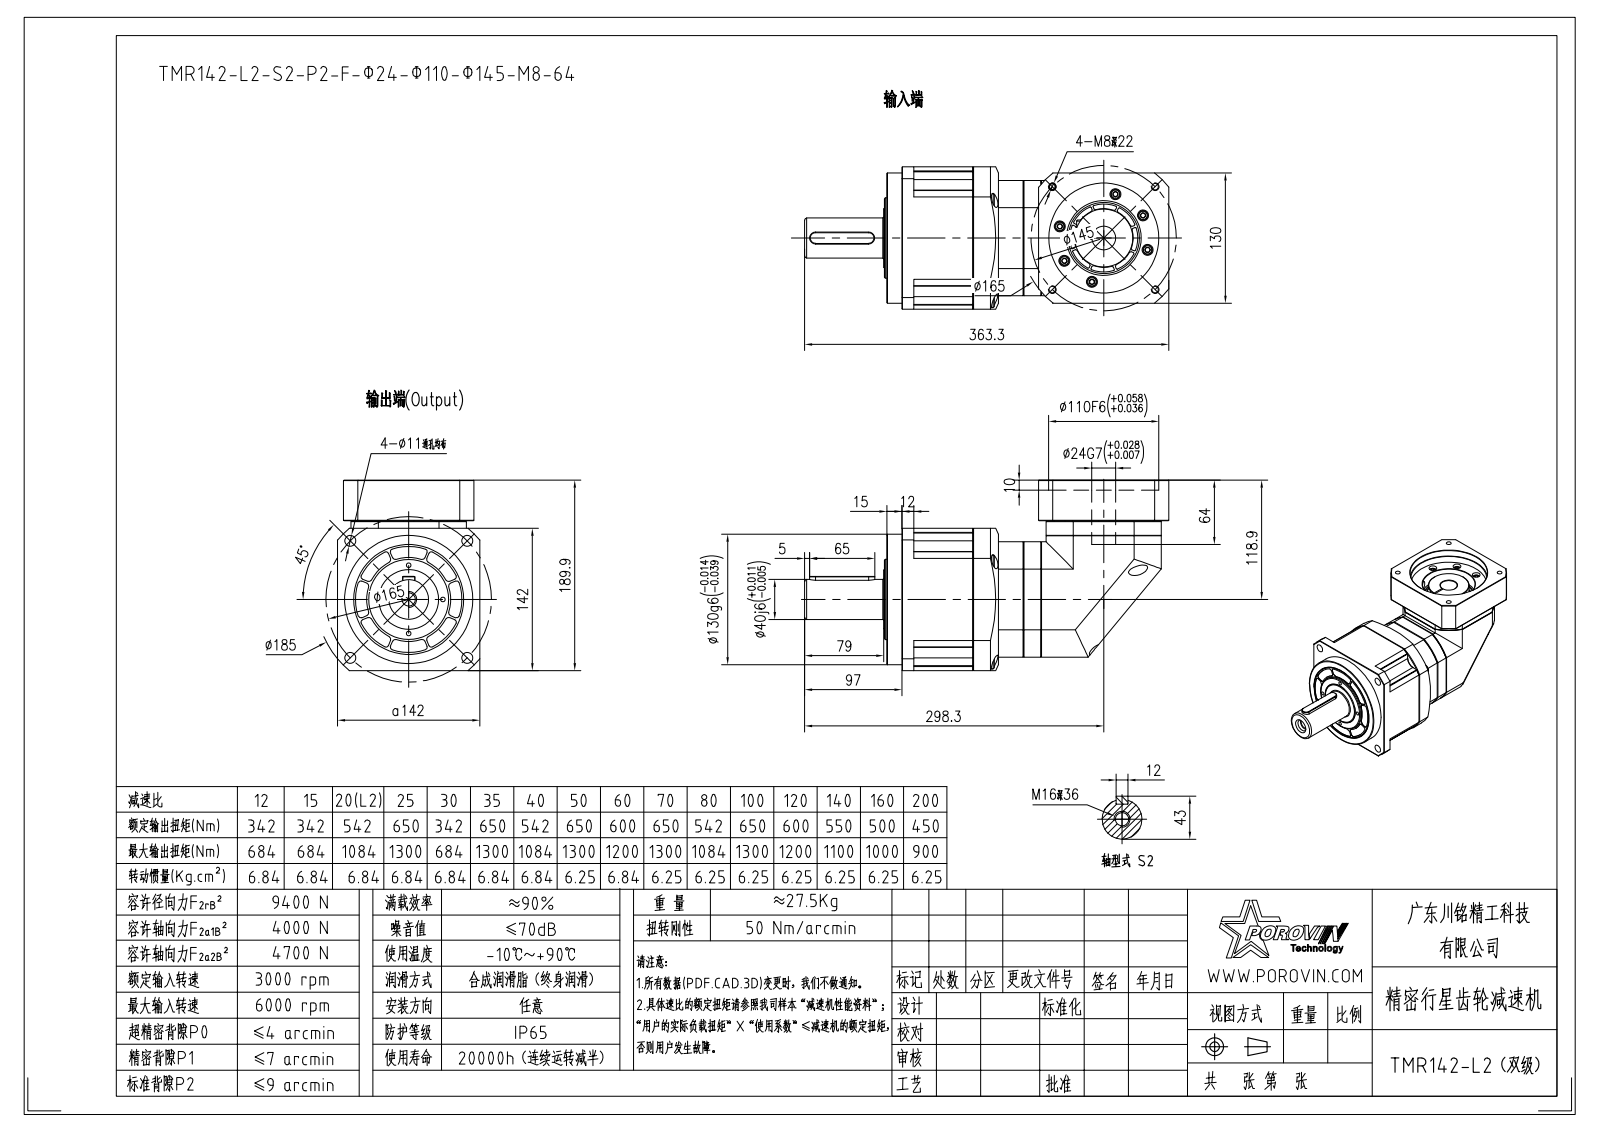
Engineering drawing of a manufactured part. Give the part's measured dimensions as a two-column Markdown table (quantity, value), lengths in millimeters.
| quantity | value |
| --- | --- |
| part name | HEXAGON_SOCKET_HEAD_CAP_S-10700; SPRING_LOCK_WASHERS--NORMAL_TYP; HEXAGON_SOCKET_HEAD_CAP_S-10760; TMR1150003 (+8 more) |
| STEP written by | CREO PARAMETRIC BY PTC INC, 2020053 (CONFIG_CONTROL_DESIGN) |
| units | millimeters |
| bodies | 47 solids, 1467 faces (614 planar, 572 cylindrical, 281 other) |
| overall size | 363.3 × 189.9 × 142 |
| volume | 4 142 000 mm³ |
| surface area | 431 251 mm² |
| round holes (diameter × count) | 6.68 × 16, 5 × 13, 11 × 12, 6.8 × 11, 6.5 × 10, 6.6 × 6, 14 × 5, 9 × 4, 10.5 × 4, 11.9 × 4, 8.5 × 1, 13.6 × 1 |
| round bosses / shafts (diameter × count) | 10 × 16, 9.88 × 16, 6 × 16, 13 × 5, 8 × 5, 130 × 1, 99 × 1, 80 × 1 |
| partial cylindrical surfaces (radius × count) | 1 × 40, 2 × 32, 10.5 × 4, 6 × 2, 65 × 2, 5 × 1, 6.75 × 1, 42.5 × 1 |
| main face-to-face distances | 13.5, 128.5, 50.3, 18, 7.5, 68.3, 68.1, 17.8, 142, 115 |
| hole center spacings | 45.25, 111.28, 12.31, 21.17, 47.5, 51.41, 91.96, 110.07 |
